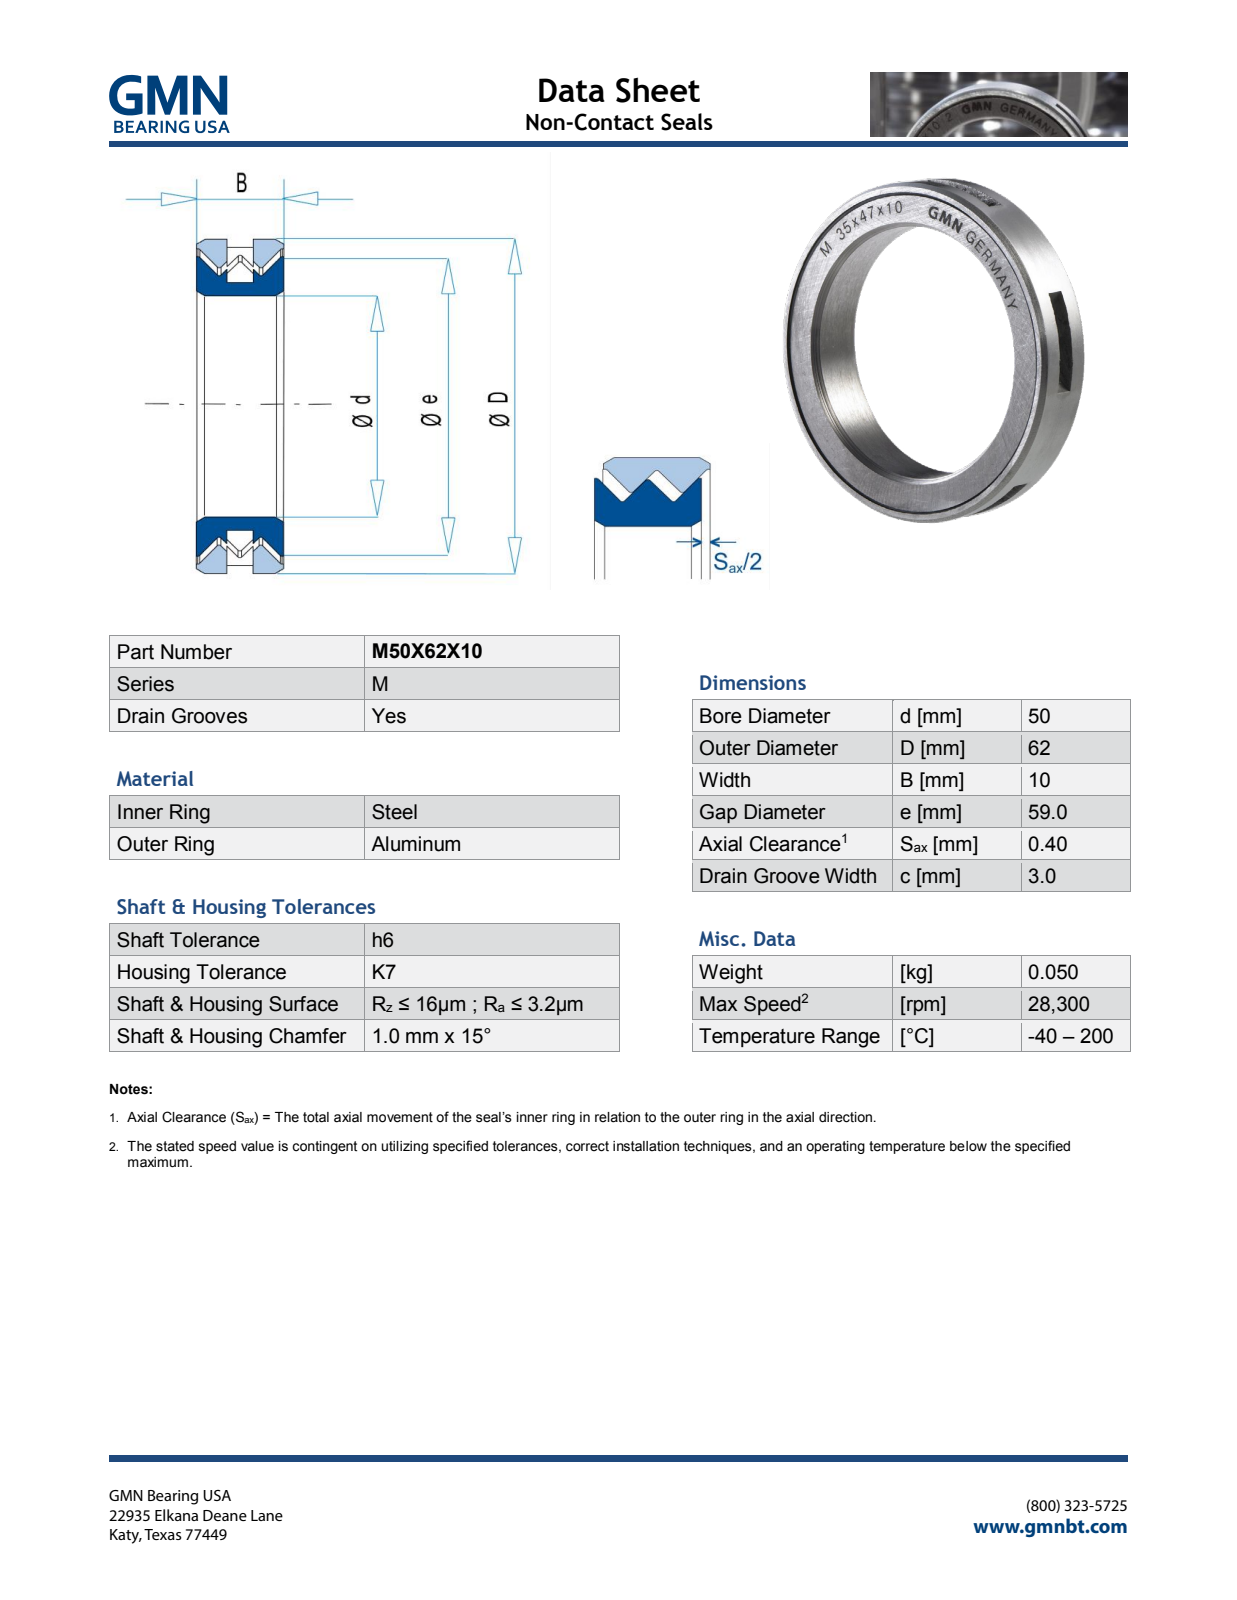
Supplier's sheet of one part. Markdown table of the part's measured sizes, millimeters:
| quantity | value |
| --- | --- |
| part name | M50X62X10_PRT |
| STEP written by | PRO/ENGINEER BY PARAMETRIC TECHNOLOGY CORPORATION, 2013150 (AUTOMOTIVE_DESIGN) |
| units | millimeters |
| bodies | 2 solids, 647 faces (570 planar, 27 cylindrical, 50 other) |
| overall size | 62 × 62 × 10.07 |
| volume | 9 338 mm³ |
| surface area | 10 100 mm² |
| round holes (diameter × count) | 50 × 1, 59.28 × 1 |
| round bosses / shafts (diameter × count) | 62 × 1, 59 × 1 |
| partial cylindrical surfaces (radius × count) | 10 × 5 |
| main face-to-face distances | 10, 3.5, 6.5, 3, 3.57, 6.57, 10.07, 1.68, 1.92, 1.44 |
